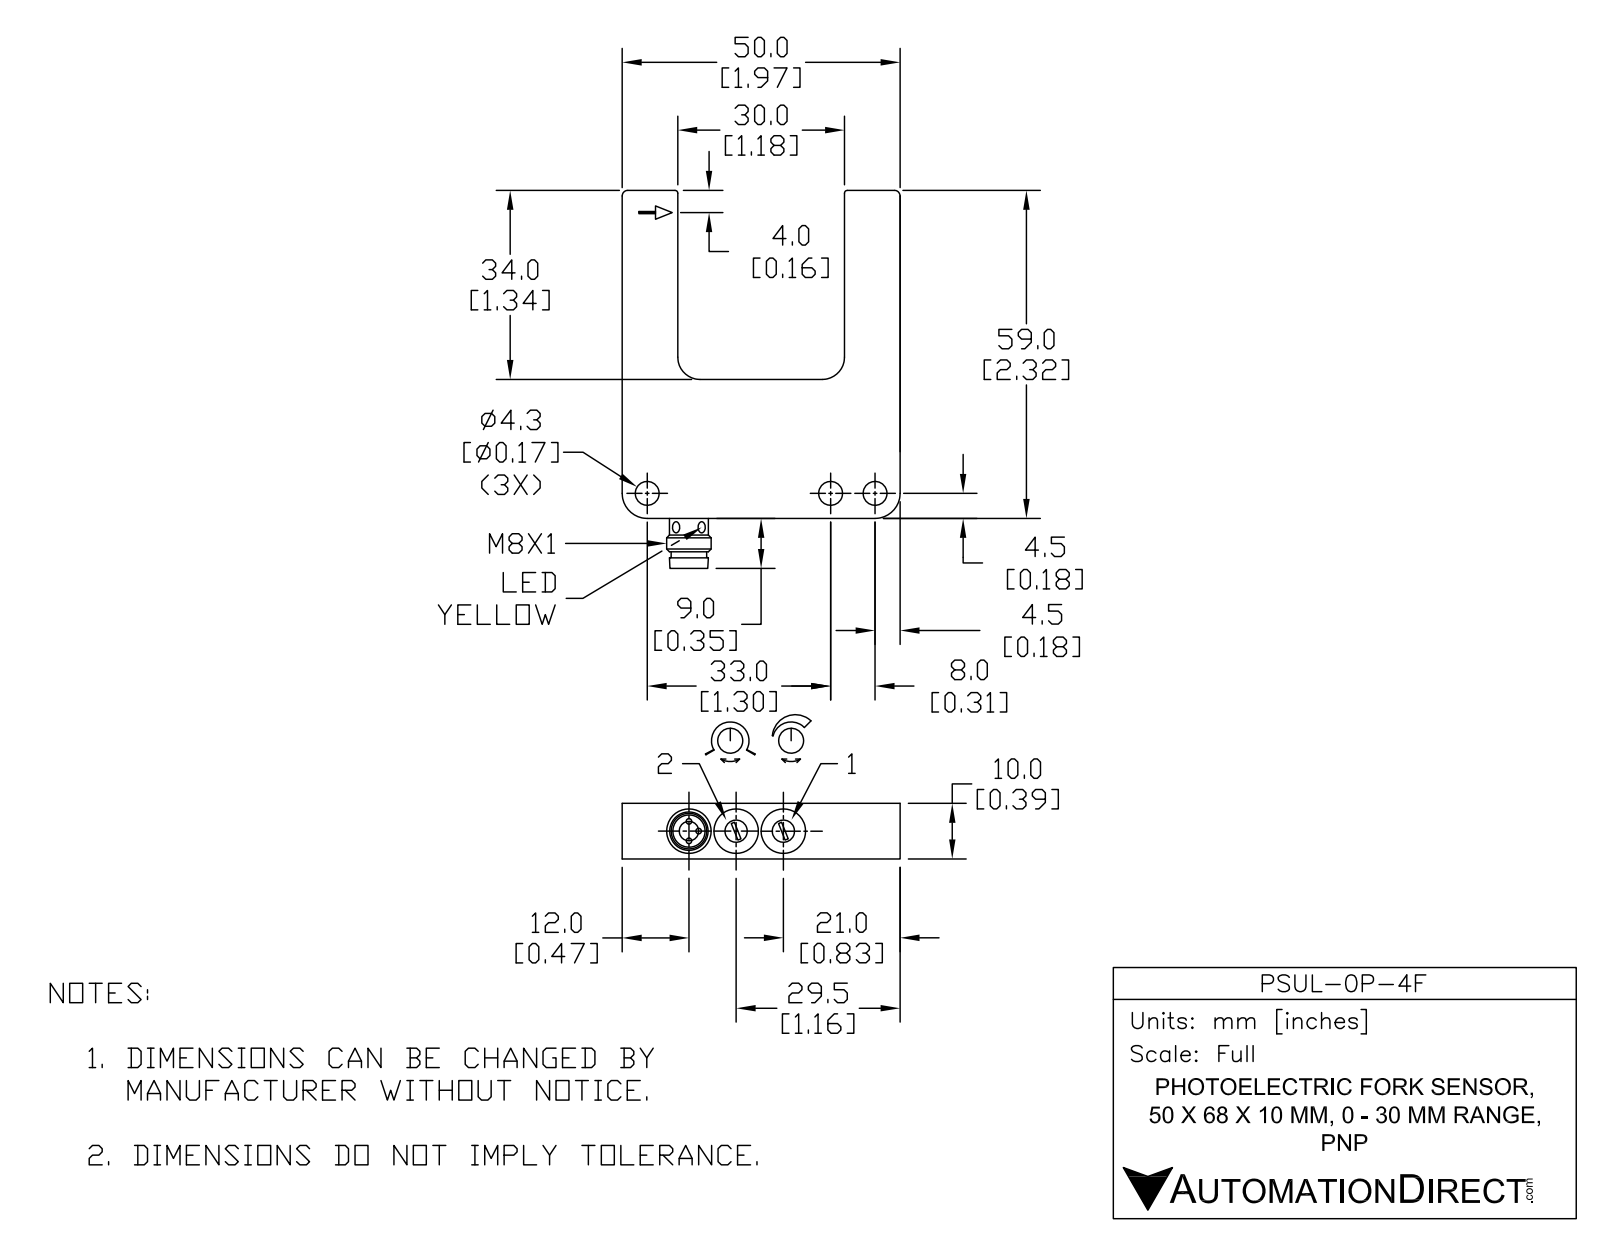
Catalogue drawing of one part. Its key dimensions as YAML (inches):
part_name: "PSUL-0P-4F"
step_written_by: "SolidWorks 2016 (AUTOMOTIVE_DESIGN)"
units: inches
bodies: {solids: 1, faces: 83, planar: 35, cylindrical: 42, other: 6}
overall_size: [2.677, 1.969, 0.394]
volume: 1.162
surface_area: 11.28
round_holes:
  - {diameter: 0.169, count: 3}
  - {diameter: 0.079, count: 2}
  - {diameter: 0.157, count: 2}
  - {diameter: 0.315, count: 2}
  - {diameter: 0.228, count: 1}
round_bosses_or_shafts:
  - {diameter: 0.315, count: 1}
  - {diameter: 0.267, count: 1}
partial_cylinders:
  - {radius: 0.02, count: 2}
  - {radius: 0.039, count: 2}
  - {radius: 0.063, count: 2}
  - {radius: 0.157, count: 2}
  - {radius: 0.177, count: 2}
face_to_face_distances: [0.394, 1.575, 1.969, 1.181, 0.984, 1.339, 2.323, 2.319, 0.98, 0.157]
hole_center_spacings: [0.335, 0.315, 0.669, 1.299, 1.614]
